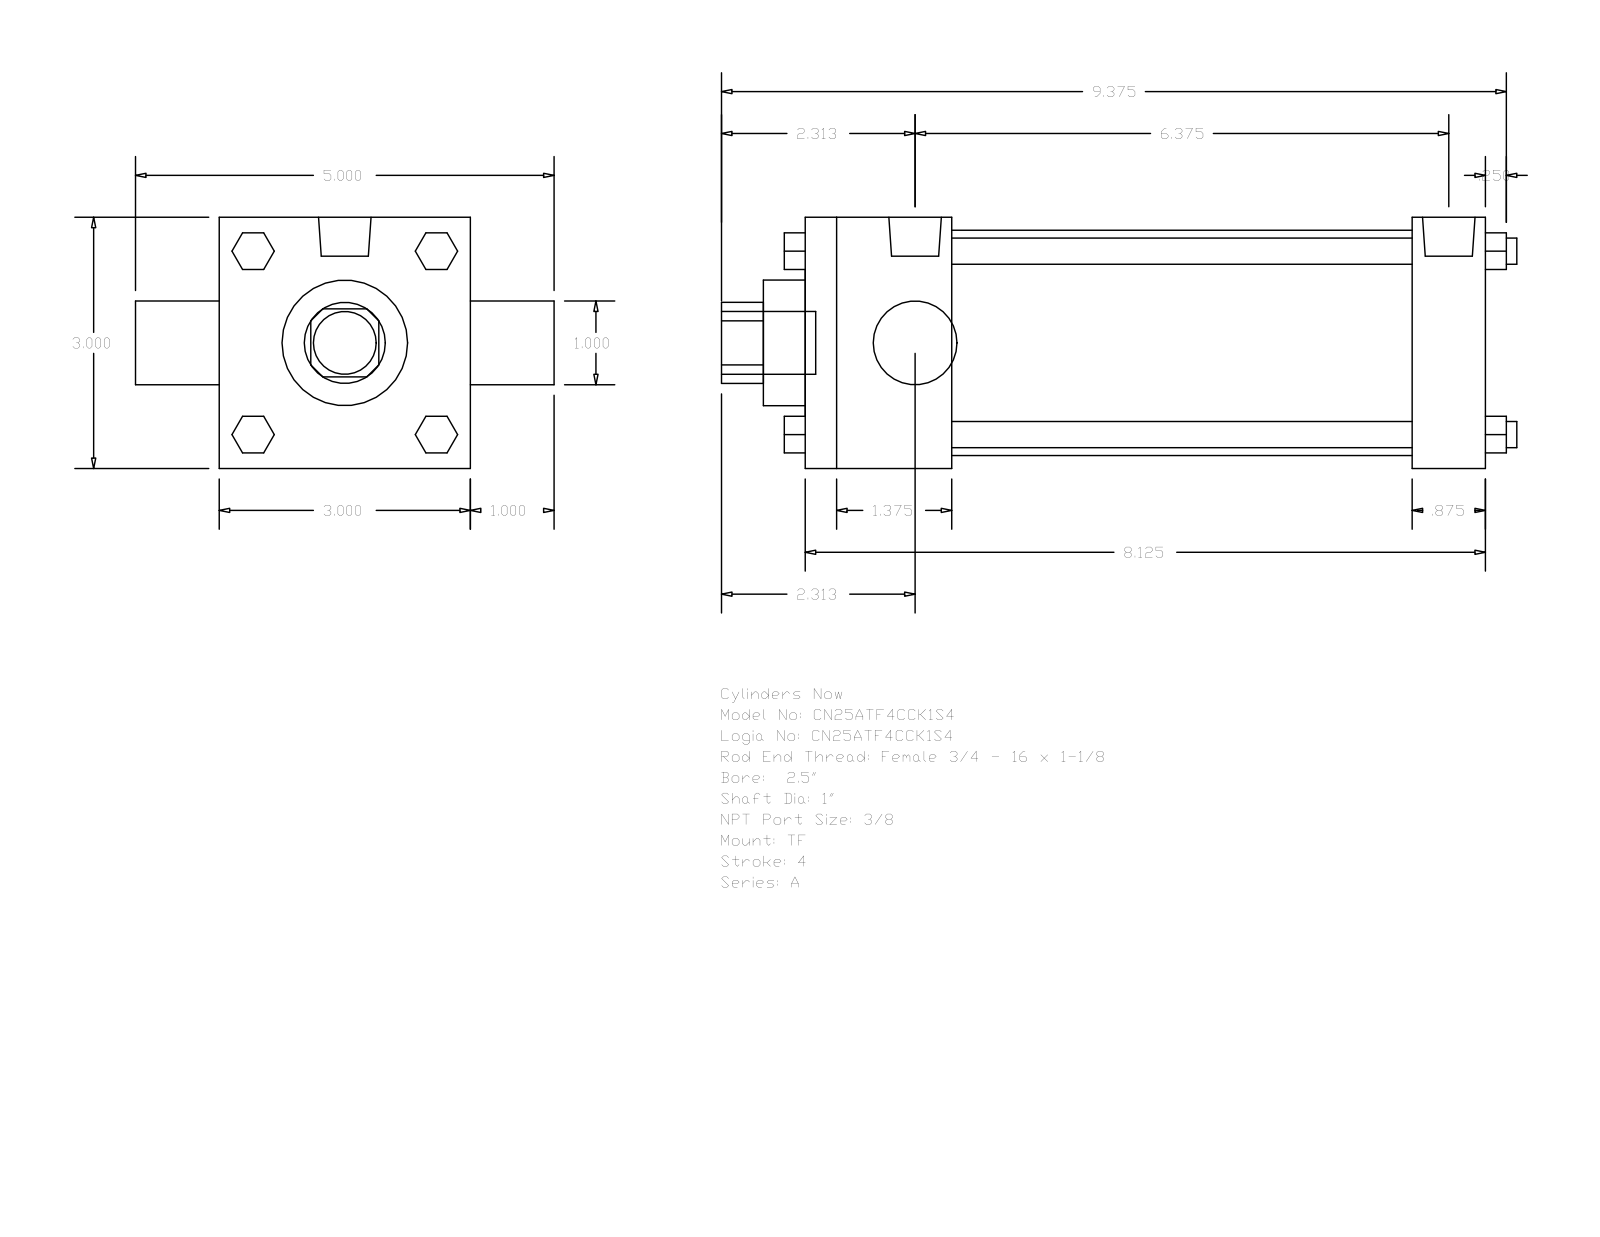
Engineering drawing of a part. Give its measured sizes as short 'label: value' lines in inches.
name: A_TF__0250_1
written by: GSSL Pune (CONFIG_CONTROL_DESIGN)
unit: in
bodies: 0 solids, 120 faces (92 planar, 28 cylindrical, 0 other)
size: 9.5 × 5 × 3
holes: 2× ⌀1, 1× ⌀1.5, 1× ⌀2.69
bosses: 4× ⌀0.313, 3× ⌀0.219, 2× ⌀0.627, 1× ⌀0.75
rounds: 1× R0.484
face distances: 3, 8.125, 1.75, 7.25, 5.5, 6.375, 0.875, 1, 4, 0.5
